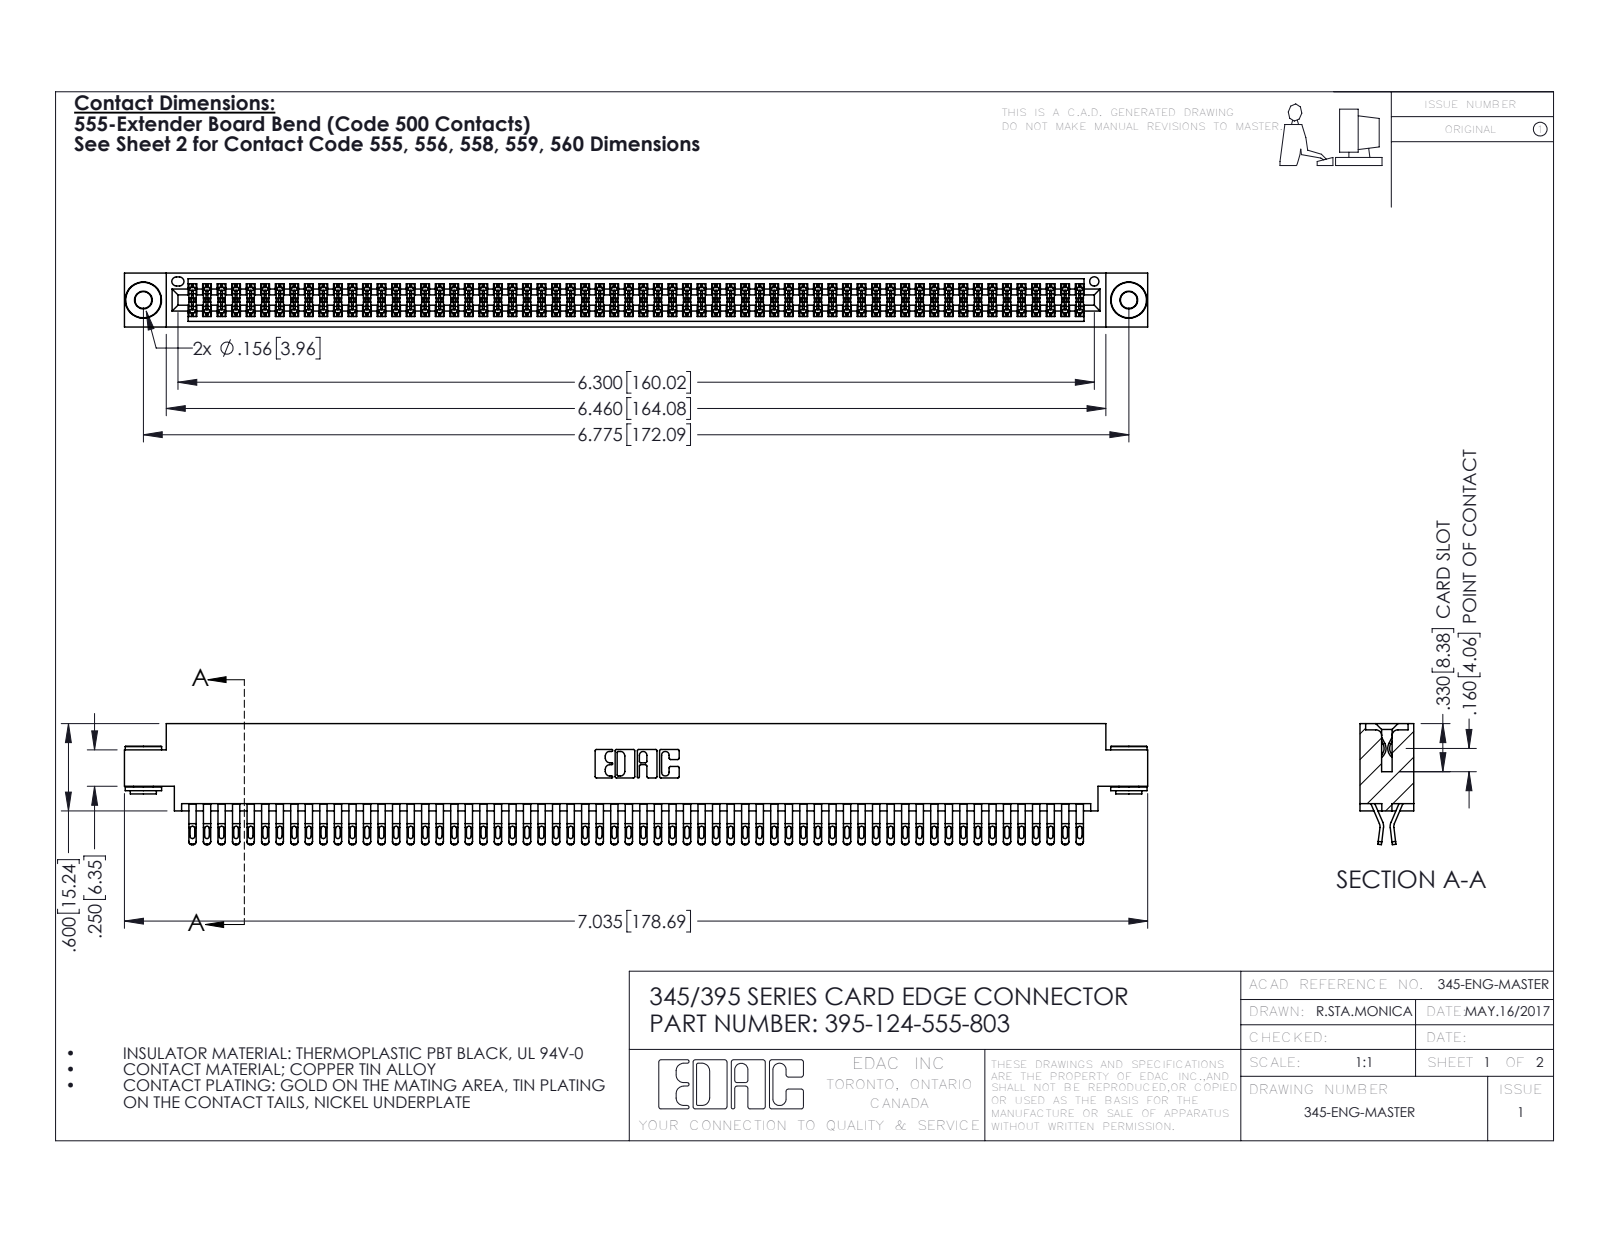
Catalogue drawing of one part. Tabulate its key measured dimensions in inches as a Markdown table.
| quantity | value |
| --- | --- |
| part name | 345 Part_0.170 Offset - 0.156 Dia-TH; 395-124-555-803; 345-292-001_555 Tail; 345-250-002_345-250-002-102 |
| STEP written by | SolidWorks 2016 (CONFIG_CONTROL_DESIGN) |
| units | inches |
| bodies | 127 solids, 7112 faces (3938 planar, 3166 cylindrical, 8 other) |
| overall size | 7.035 × 0.832 × 0.37 |
| volume | 1.087 in³ |
| surface area | 43.88 in² |
| round holes (diameter × count) | 0.116 × 2, 0.156 × 2, 0.064 × 1 |
| round bosses / shafts (diameter × count) | 0.25 × 2, 0.18 × 2, 0.136 × 2 |
| partial cylindrical surfaces (radius × count) | 0.016 × 310, 0.02 × 248, 0.006 × 186, 0.01 × 22, 0.007 × 6, 0.031 × 6, 0.026 × 3, 0.01 × 2 |
| main face-to-face distances | 0.072, 0.298, 0.37, 0.025, 0.2, 0.098, 0.272, 0.225, 0.175, 0.149 |
| hole center spacings | 0.27, 6.539, 6.775 |
